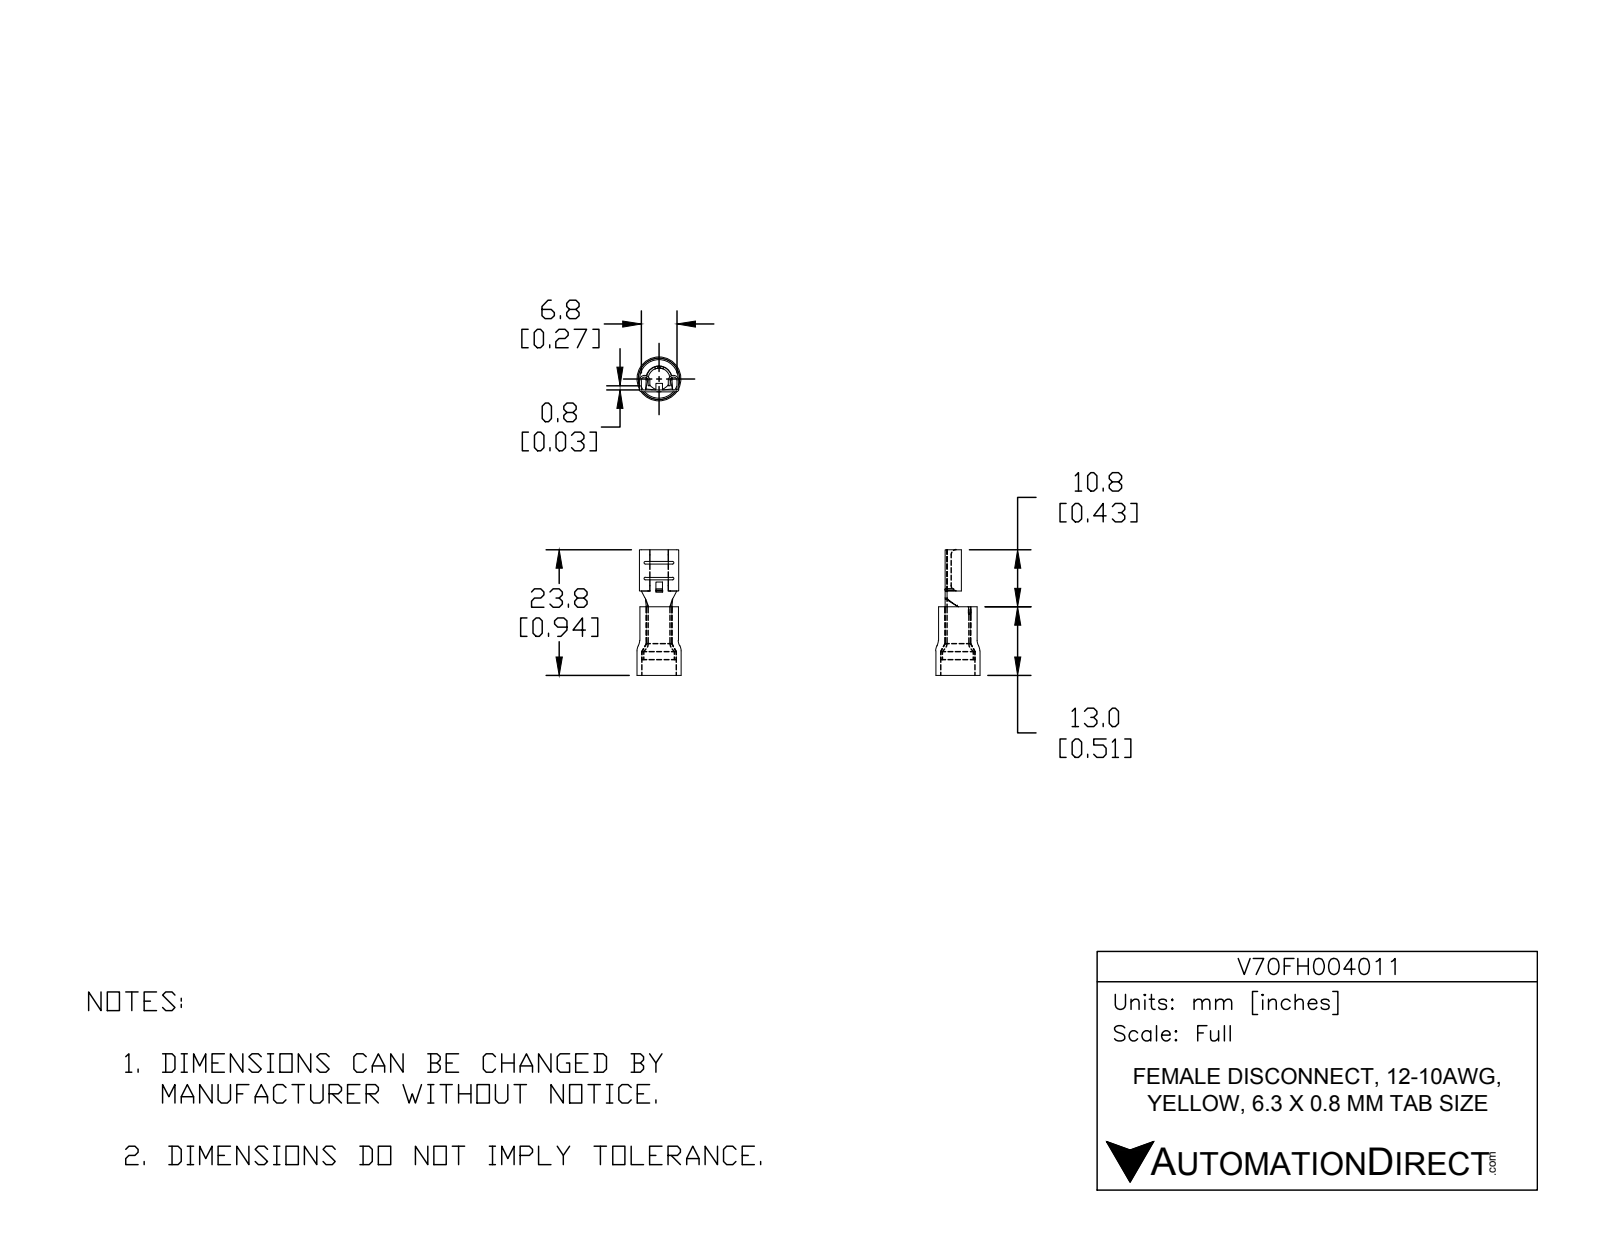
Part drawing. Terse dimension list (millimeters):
name: V70FH004011
written by: SolidWorks 2017 (AUTOMOTIVE_DESIGN)
unit: mm
bodies: 2 solids, 102 faces (36 planar, 42 cylindrical, 24 other)
size: 23.8 × 8.35 × 8.35
volume: 407 mm³; area: 1 242 mm²
holes: 1× ⌀4.13, 1× ⌀5.8, 1× ⌀6.5
bosses: 1× ⌀8.35, 1× ⌀7.3, 1× ⌀4.83
rounds: 6× R0.25, 4× R0.5, 4× R1, 2× R0.38, 2× R0.65
face distances: 0.35, 1.65, 5.46, 7.11, 13, 2, 5.81, 1.3, 5.11, 3.81
